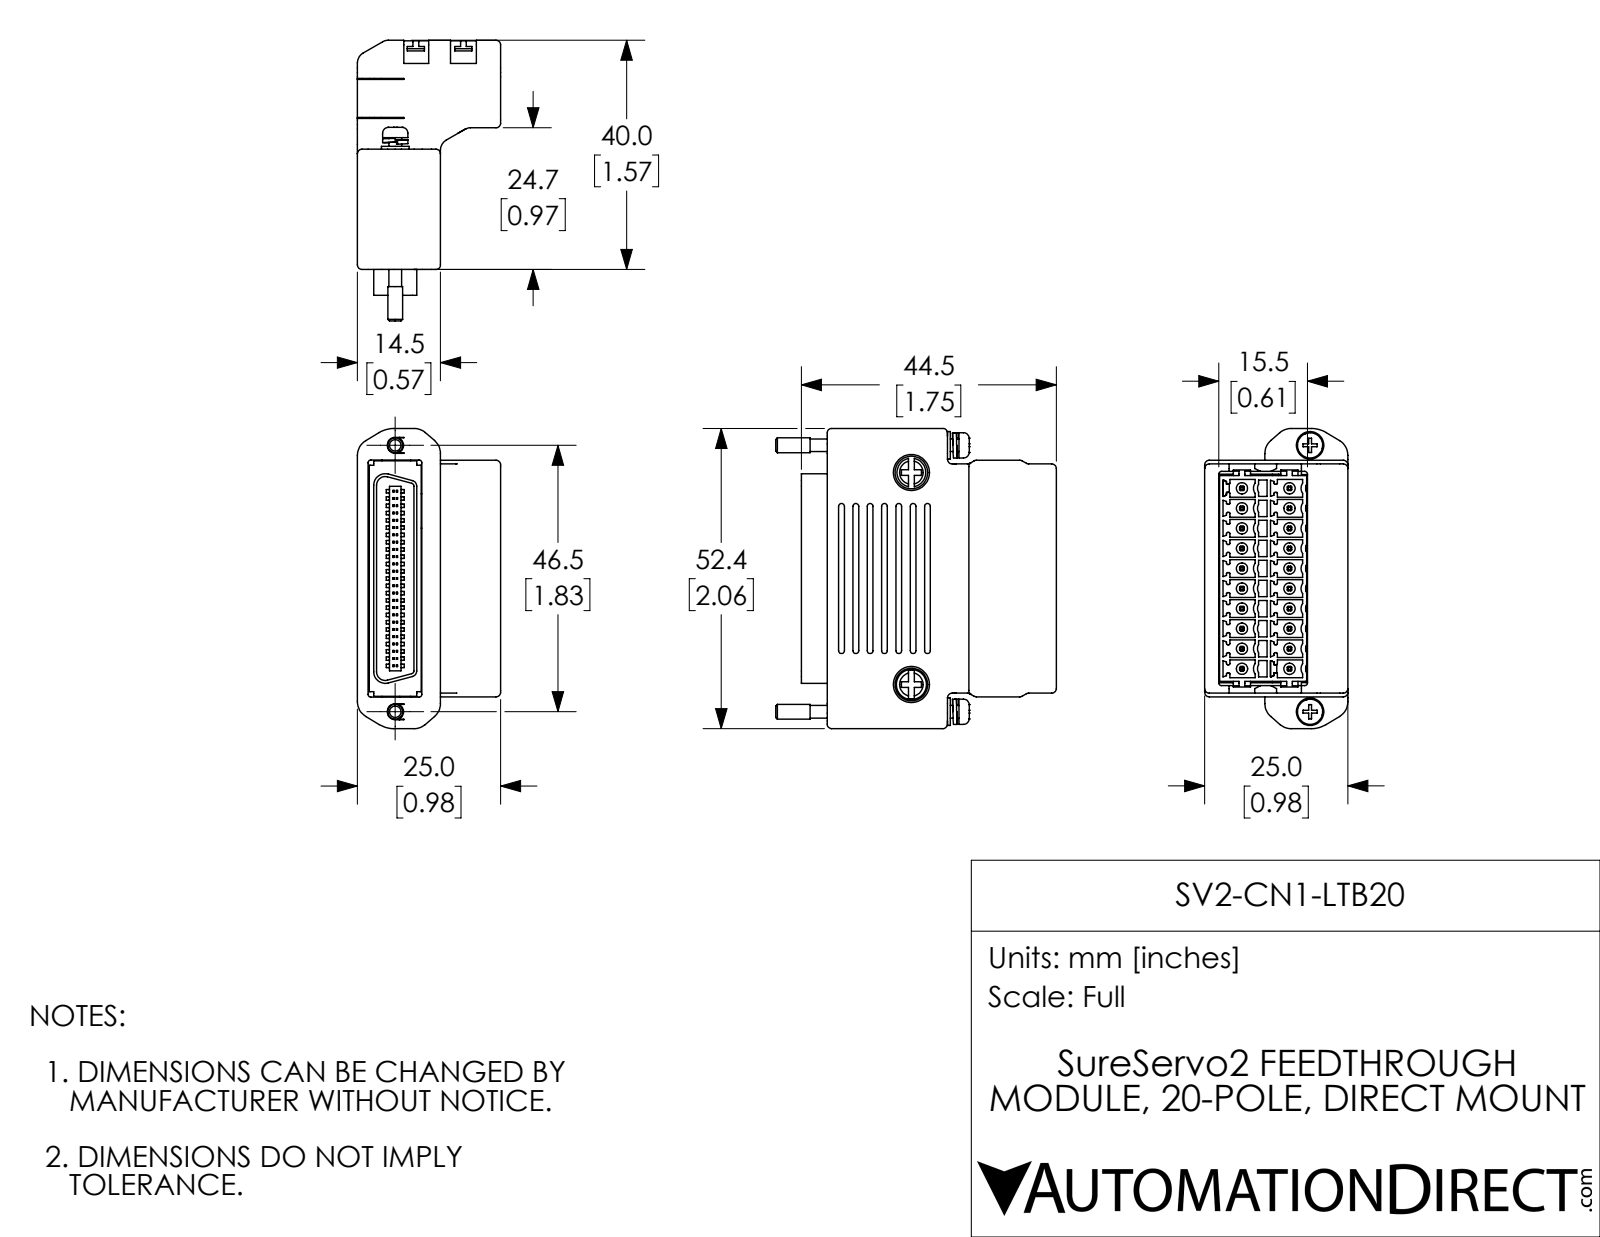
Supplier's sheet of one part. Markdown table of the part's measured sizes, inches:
| quantity | value |
| --- | --- |
| part name | SV2-CN1-LTB20 |
| STEP written by | SolidWorks 2017 (AUTOMOTIVE_DESIGN) |
| units | inches |
| bodies | 10 solids, 3598 faces (2316 planar, 902 cylindrical, 380 other) |
| overall size | 2.063 × 1.929 × 0.984 |
| volume | 1.058 in³ |
| surface area | 45.93 in² |
| round holes (diameter × count) | 0.043 × 20, 0.094 × 2, 0.224 × 2, 0.059 × 1, 0.106 × 1, 0.126 × 1, 0.169 × 1, 0.213 × 1 |
| round bosses / shafts (diameter × count) | 0.287 × 2, 0.189 × 2, 0.173 × 2, 0.102 × 2, 0.087 × 2, 0.29 × 1, 0.207 × 1, 0.201 × 1 |
| partial cylindrical surfaces (radius × count) | 0.008 × 244, 0.031 × 54, 0.02 × 45, 0.062 × 15, 0.062 × 15, 0.012 × 13, 0.059 × 10, 0.039 × 6 |
| main face-to-face distances | 0.039, 0.051, 0.232, 0.272, 0.276, 0.52, 0.327, 0.193, 0.081, 0.031 |
| hole center spacings | 0.138, 0.195, 0.276, 0.308, 0.413, 0.436, 0.551, 0.568 |
